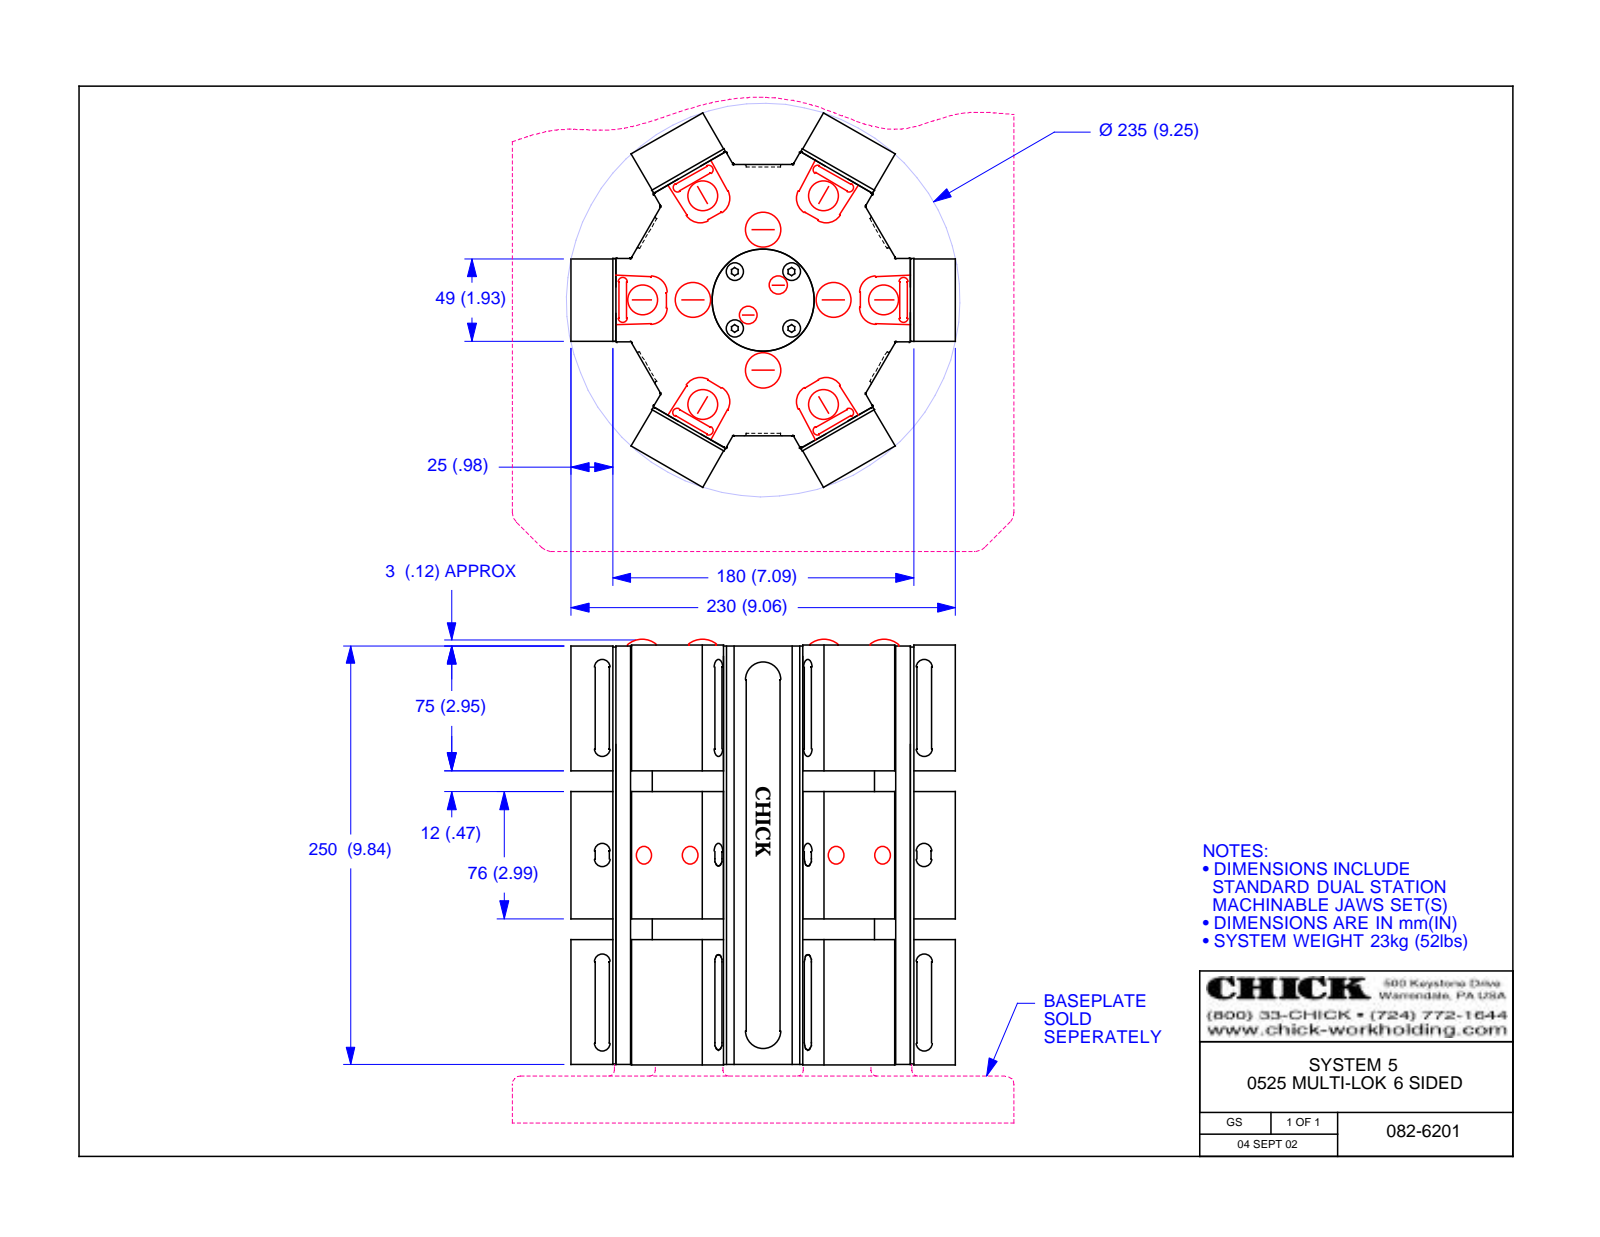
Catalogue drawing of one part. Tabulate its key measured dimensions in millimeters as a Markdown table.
| quantity | value |
| --- | --- |
| part name | 082-6201; 082-6211; 5CP0525-ST; 080-2505 (+2 more) |
| STEP written by | Autodesk Inventor 2013 (AUTOMOTIVE_DESIGN) |
| units | millimeters |
| bodies | 25 solids, 2950 faces (1507 planar, 638 cylindrical, 805 other) |
| overall size | 254 × 230 × 223.3 |
| volume | 6 693 000 mm³ |
| surface area | 717 994 mm² |
| round holes (diameter × count) | 12.7 × 30, 5.2 × 10, 9.65 × 10, 9.14 × 6, 10.11 × 6, 10 × 5, 20 × 4, 4.06 × 3, 6.87 × 3, 50 × 1, 60 × 1 |
| round bosses / shafts (diameter × count) | 14 × 18, 10 × 18, 7.67 × 3, 4.76 × 3 |
| partial cylindrical surfaces (radius × count) | 0.8 × 172, 1 × 24, 0.4 × 20, 1.2 × 20, 1.9 × 12, 7.9 × 12, 11.11 × 12, 1.65 × 6 |
| main face-to-face distances | 2, 178, 25, 27, 203, 205, 176, 180, 17.7, 31.7 |
| hole center spacings | 100, 105, 104.99, 32, 32.01, 200, 31.99, 202.54 |
